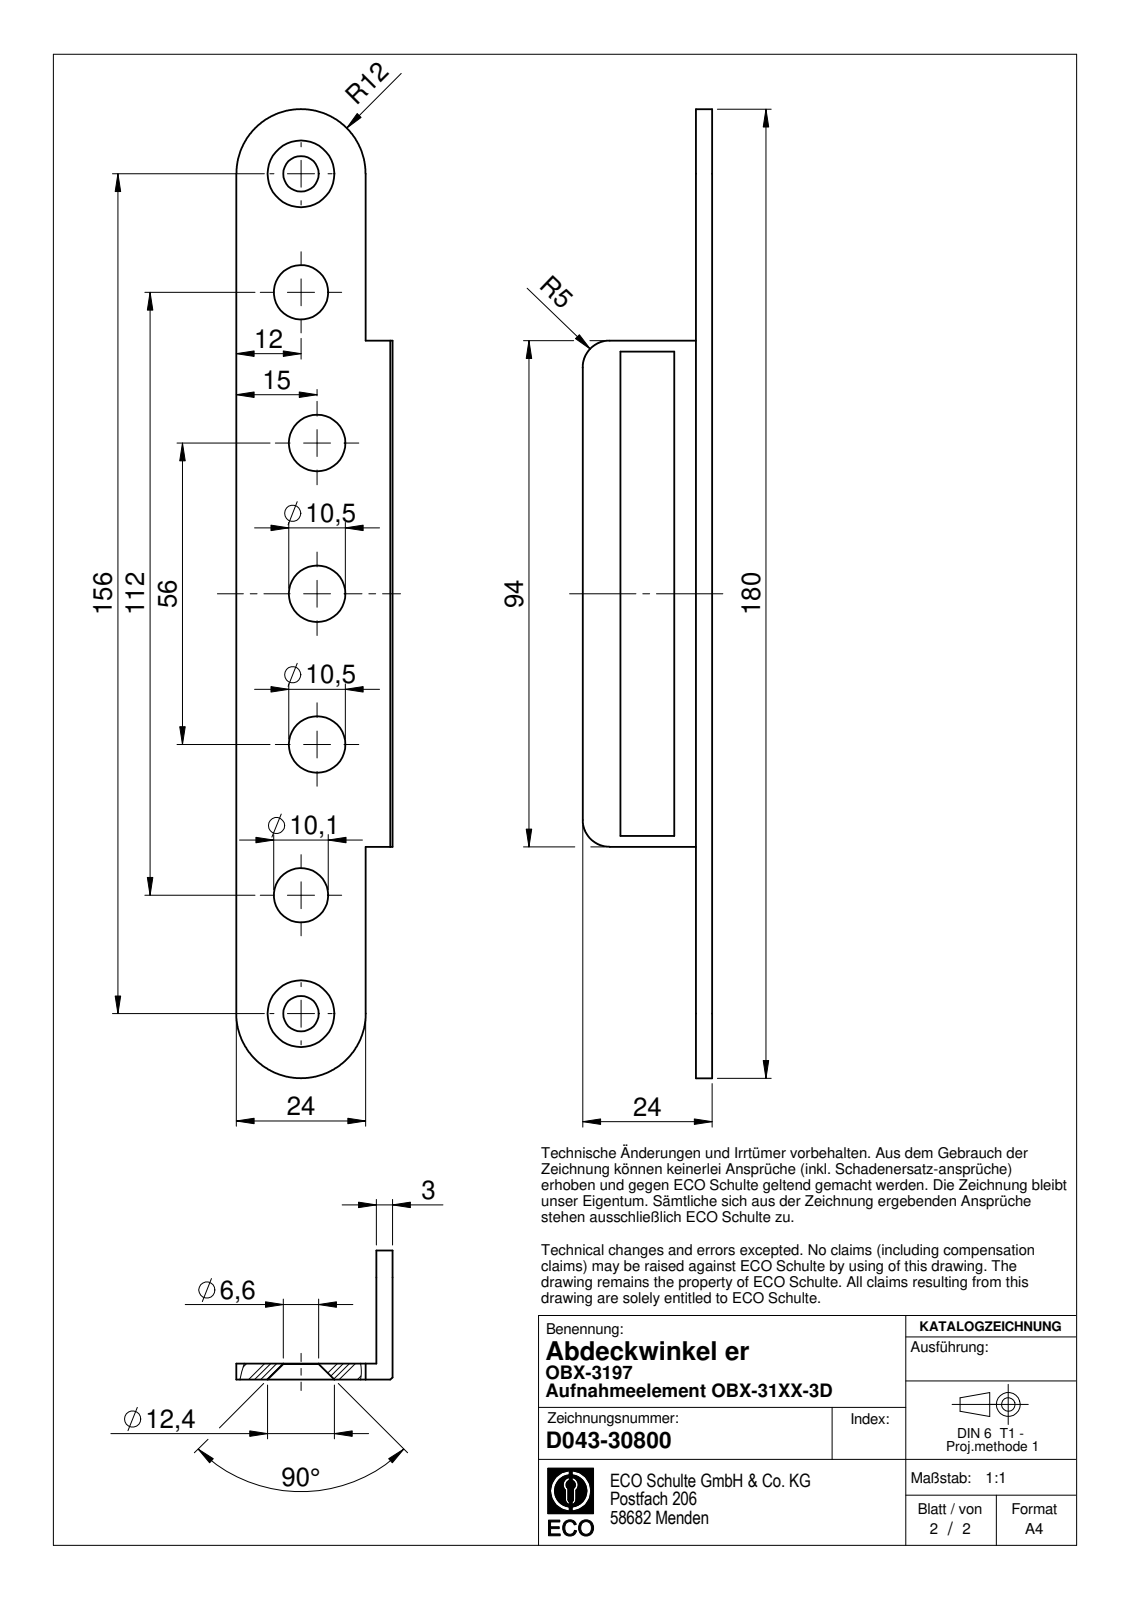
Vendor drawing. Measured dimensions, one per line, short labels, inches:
name: OBX-3197-er_D043-30800
written by: SolidWorks 2020 (AUTOMOTIVE_DESIGN)
unit: in
bodies: 1 solid, 37 faces (15 planar, 18 cylindrical, 4 other)
size: 7.087 × 1.142 × 0.945
volume: 0.945 in³; area: 20.04 in²
holes: 3× ⌀0.413, 2× ⌀0.26, 2× ⌀0.398
rounds: 2× R0.197, 2× R0.472
face distances: 0.118, 0.276, 0.669, 1.024, 1.142, 0.945, 0.157, 0.394, 0.551, 0.827
hole spacings: 0.866, 1.102, 1.109, 1.972, 2.208, 3.073, 3.309, 4.175
